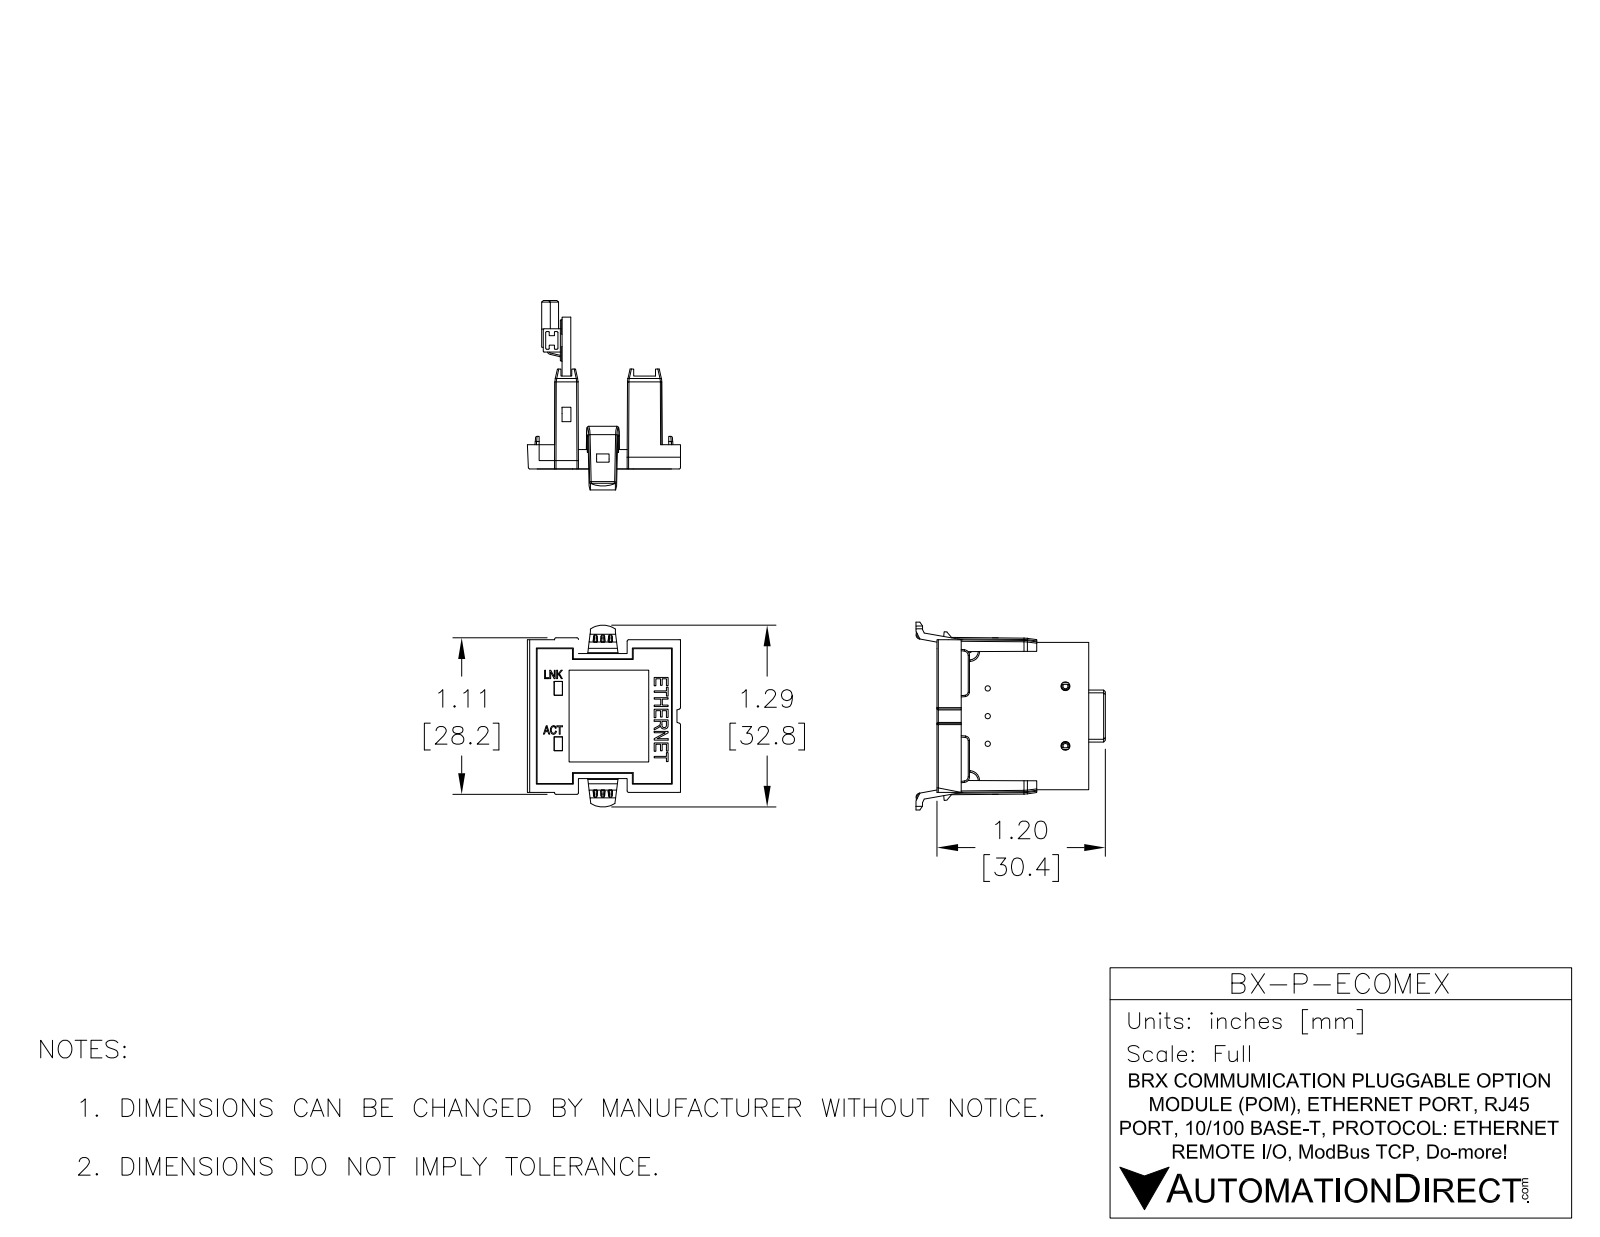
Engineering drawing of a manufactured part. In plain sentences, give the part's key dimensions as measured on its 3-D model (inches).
The part is named "BX-P-ECOMLC". Its 3-D file was written by "SolidWorks 2017 (AUTOMOTIVE_DESIGN)". It is 48 solids with 1826 faces: 1529 planar, 253 cylindrical and 44 other. Overall it measures 1.335 by 1.334 by 1.084 inches. Its volume is 0.39 cubic inches and its surface area 14.63 square inches. Round holes: 3 of diameter 0.037, 2 of diameter 0.063. Round bosses or shafts: 2 of diameter 0.118. Partial cylindrical surfaces (rounded edges, fillets, slot ends): 47 of radius 0.008, 42 of radius 0.004, 10 of radius 0.033, 8 of radius 0.01, 6 of radius 0.016, 5 of radius 0.049, 4 of radius 0.006, 4 of radius 0.108. The main face-to-face distances are 0.062, 0.61, 0.548, 0.626, 0.066, 0.066, 0.485, 0.423, 0.125, 0.02. The hole center spacings are 0.687, 0.196, 0.197, 0.394, 0.424, 0.552, 0.553, 0.591.
